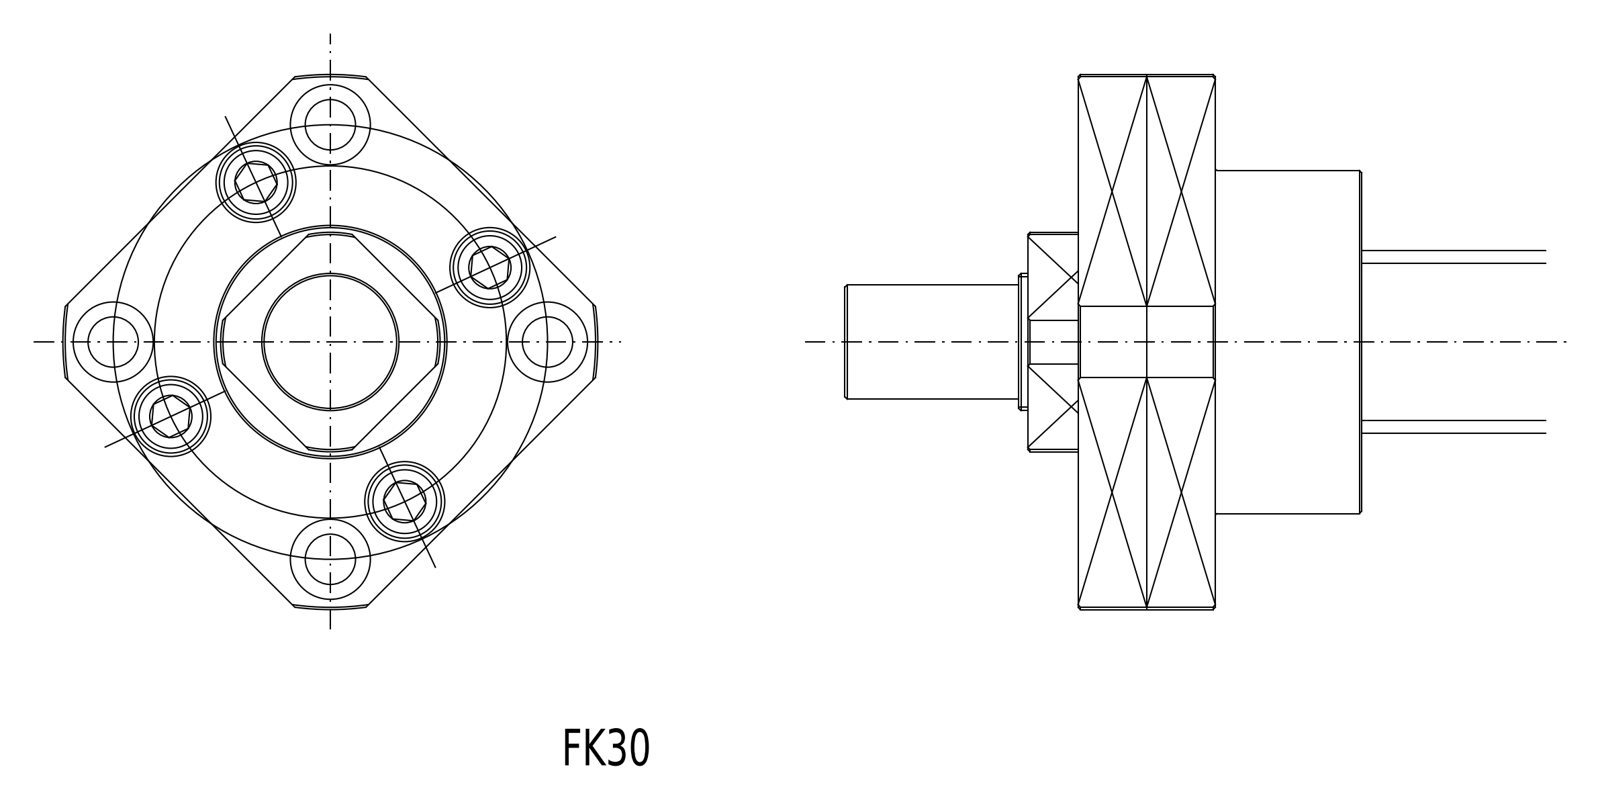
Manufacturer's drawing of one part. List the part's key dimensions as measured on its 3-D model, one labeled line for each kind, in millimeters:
Part name (STEP PRODUCT): FK30組合件
STEP written by: SolidWorks 2008 (CONFIG_CONTROL_DESIGN)
Units: millimetres
Bodies: 37 solids, 479 faces (70 planar, 151 cylindrical, 258 other)
Overall size (bounding box): 93 × 93 × 73
Volume: 277 933 mm³ · Surface area: 115 037 mm²
Round holes (diameter × count): ⌀11 ×8, ⌀8.5 ×4, ⌀17 ×4, ⌀17.5 ×4, ⌀5 ×2, ⌀28.5 ×1, ⌀30 ×1, ⌀38 ×1, ⌀50 ×1, ⌀51.3 ×1, ⌀56 ×1, ⌀63 ×1
Round bosses / shafts (diameter × count): ⌀75 ×1, ⌀74.4 ×1, ⌀62 ×1, ⌀48 ×1, ⌀40.9 ×1, ⌀40 ×1, ⌀37.1 ×1, ⌀37 ×1
Partial cylindrical surfaces — rounded edges, fillets, slot ends (radius × count): R58.5 ×1
Main face-to-face distances: 15, 32, 12, 93, 16, 30, 20, 3, 19, 50
Hole centre spacings: 20.58, 38.5, 46.83, 47.5, 54.45, 67.18, 72.7, 83.99
